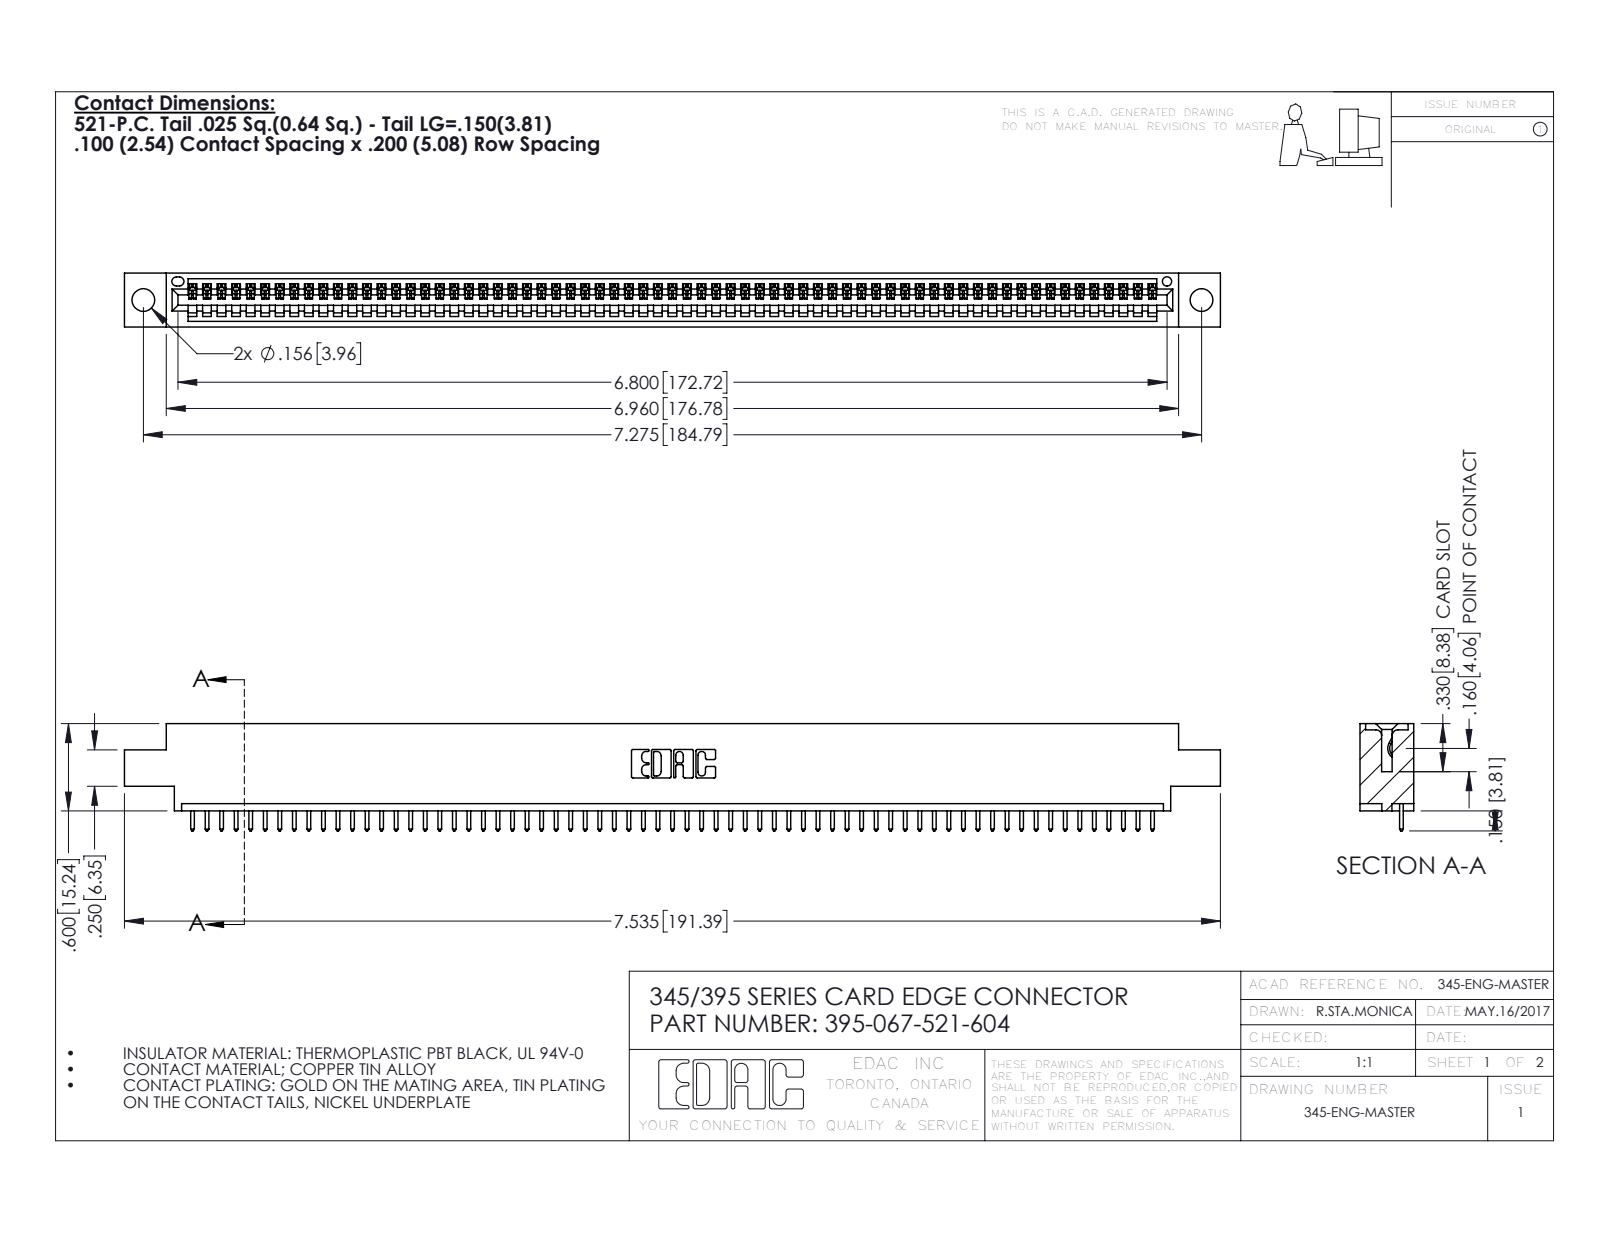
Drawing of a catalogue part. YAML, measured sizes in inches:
part_name: "345-292-001_345-293-121; 345 Part_0.170 Offset - 0.156 Dia-TH; 395-067-521-604"
step_written_by: "SolidWorks 2016 (CONFIG_CONTROL_DESIGN)"
units: inches
bodies: {solids: 68, faces: 4016, planar: 2764, cylindrical: 1252, other: 0}
overall_size: [7.535, 0.737, 0.37]
volume: 1.098
surface_area: 36.33
round_holes:
  - {diameter: 0.156, count: 2}
  - {diameter: 0.064, count: 1}
partial_cylinders:
  - {radius: 0.006, count: 134}
  - {radius: 0.01, count: 134}
  - {radius: 0.01, count: 22}
  - {radius: 0.007, count: 6}
  - {radius: 0.031, count: 6}
  - {radius: 0.026, count: 3}
  - {radius: 0.031, count: 2}
  - {radius: 0.04, count: 2}
face_to_face_distances: [0.298, 0.072, 0.37, 0.2, 0.098, 0.272, 0.025, 0.225, 0.175, 0.149]
hole_center_spacings: [0.27, 7.039, 7.275]
